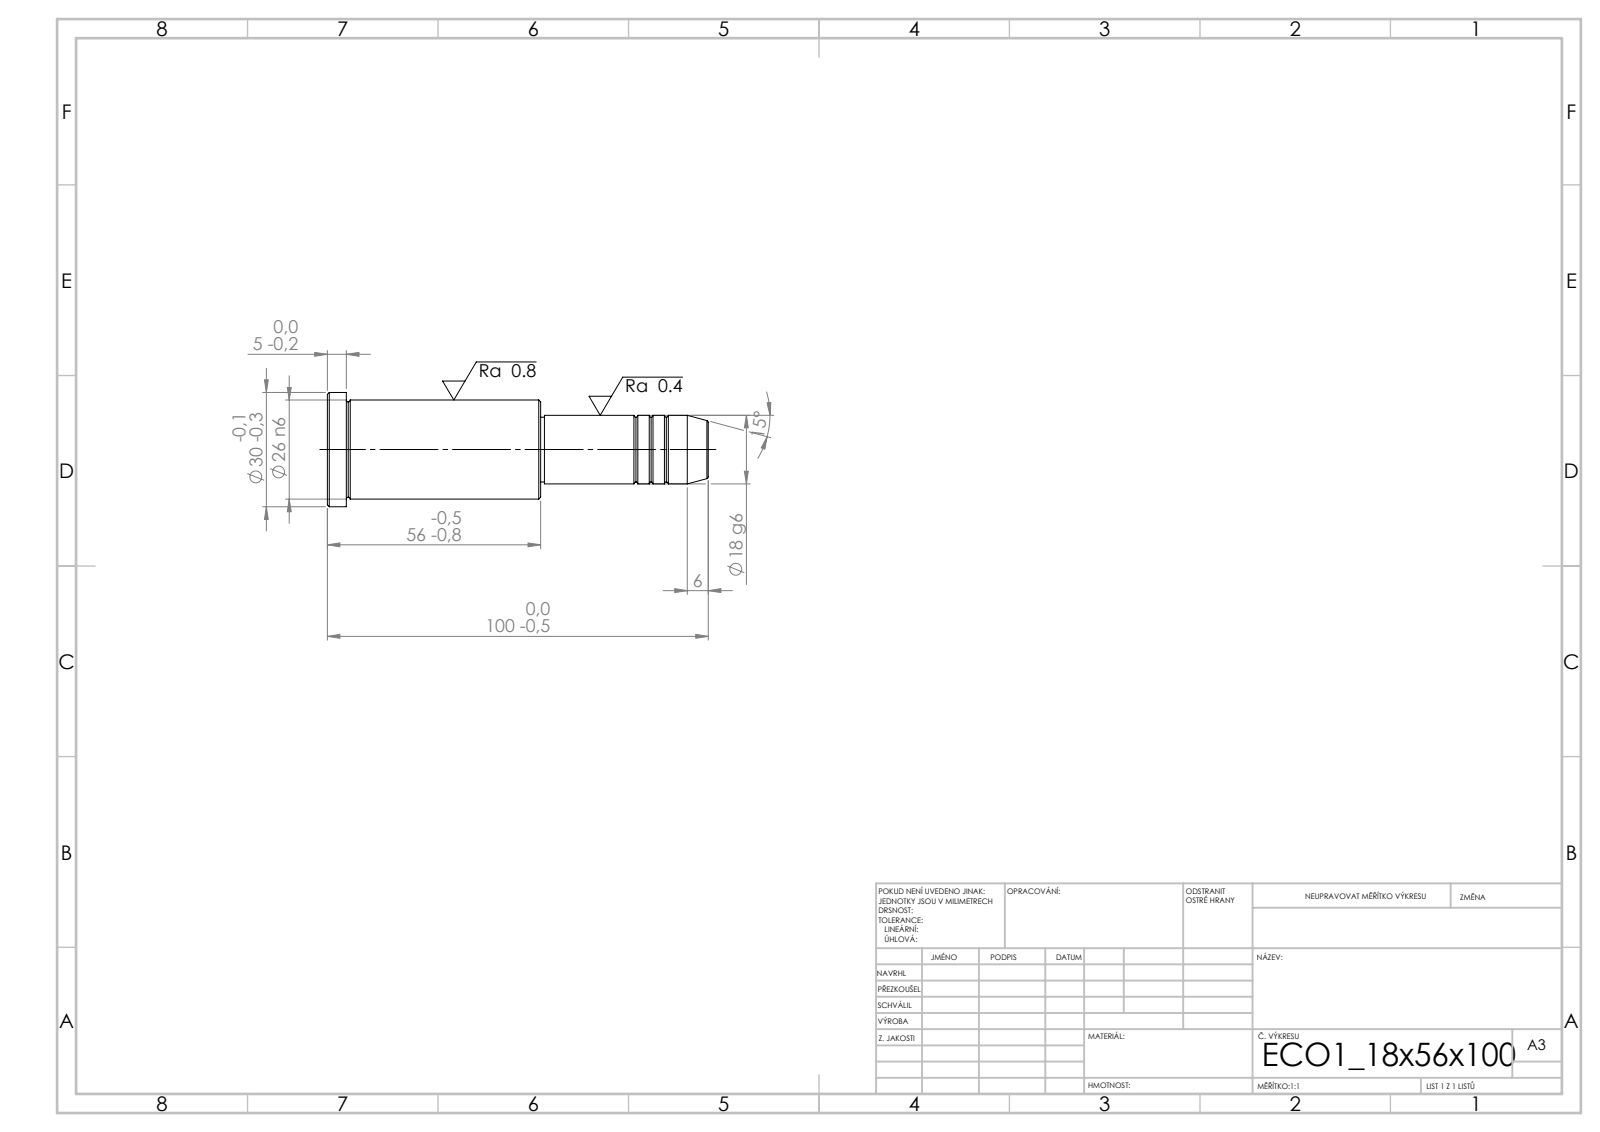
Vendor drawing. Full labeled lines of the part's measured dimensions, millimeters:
STEP written by: SolidWorks 2019 (CONFIG_CONTROL_DESIGN)
Units: millimetres
Bodies: 1 solid, 43 faces (5 planar, 14 cylindrical, 24 other)
Overall size (bounding box): 100 × 30 × 30
Volume: 41 445 mm³ · Surface area: 8 572 mm²
Round bosses / shafts (diameter × count): ⌀30 ×1, ⌀26 ×1, ⌀18 ×1, ⌀17 ×1
Main face-to-face distances: 56, 51, 5, 44, 95, 100, 43, 1, 52, 57
